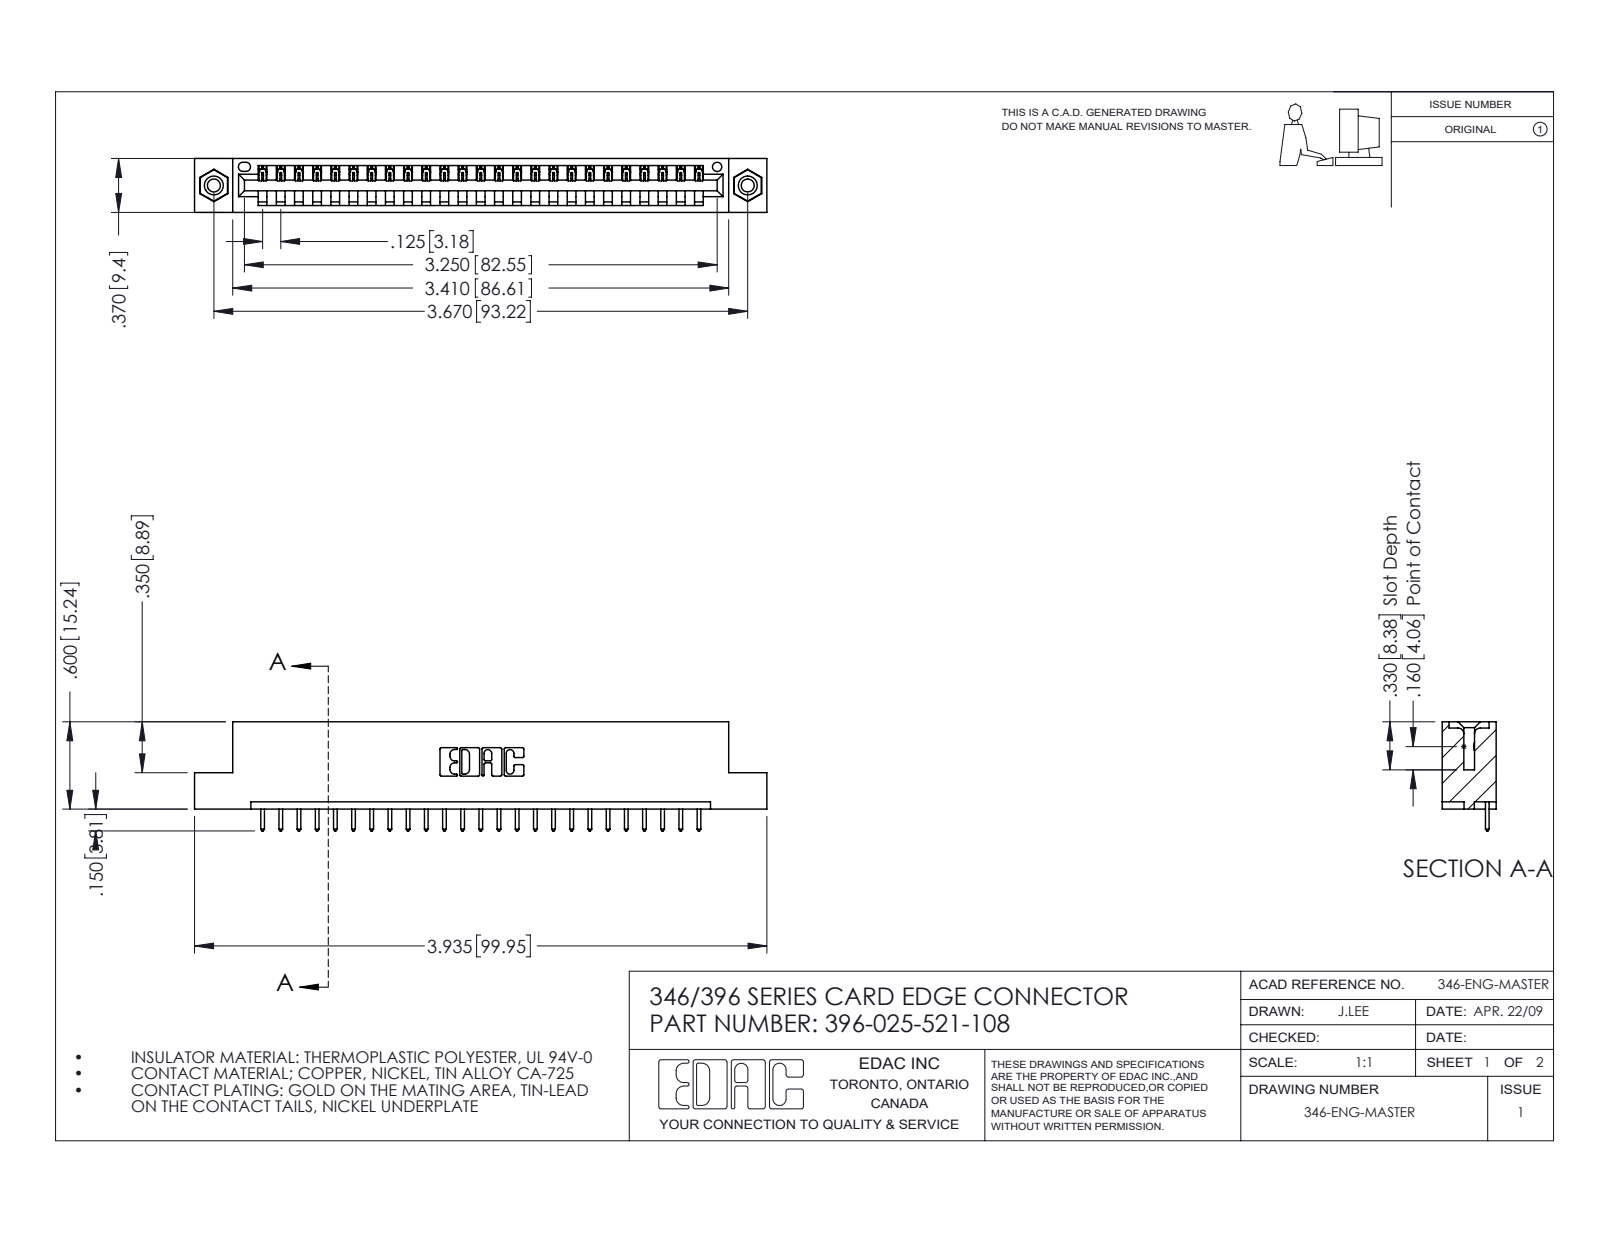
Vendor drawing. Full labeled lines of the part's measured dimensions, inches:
Part name (STEP PRODUCT): 396-025-521-108; 345-292-001_345-293-121; 345-250-001_345-250-003-102; 346 Part_Flush Mounting Lugs - 0.156 Dia-TI
STEP written by: SolidWorks 2016 (CONFIG_CONTROL_DESIGN)
Units: inches
Bodies: 28 solids, 1632 faces (1108 planar, 508 cylindrical, 16 other)
Overall size (bounding box): 3.935 × 0.75 × 0.37
Volume: 0.572 in³ · Surface area: 17.47 in²
Round holes (diameter × count): ⌀0.089 ×2, ⌀0.125 ×2, ⌀0.156 ×2, ⌀0.064 ×1
Round bosses / shafts (diameter × count): ⌀0.155 ×2
Partial cylindrical surfaces — rounded edges, fillets, slot ends (radius × count): R0.006 ×50, R0.01 ×50, R0.01 ×22, R0.007 ×6, R0.031 ×6, R0.026 ×3, R0.031 ×2, R0.04 ×2
Main face-to-face distances: 0.048, 0.322, 0.37, 0.25, 0.072, 0.298, 0.025, 0.148, 0.222, 0.1
Hole centre spacings: 0.246, 3.462, 3.67
